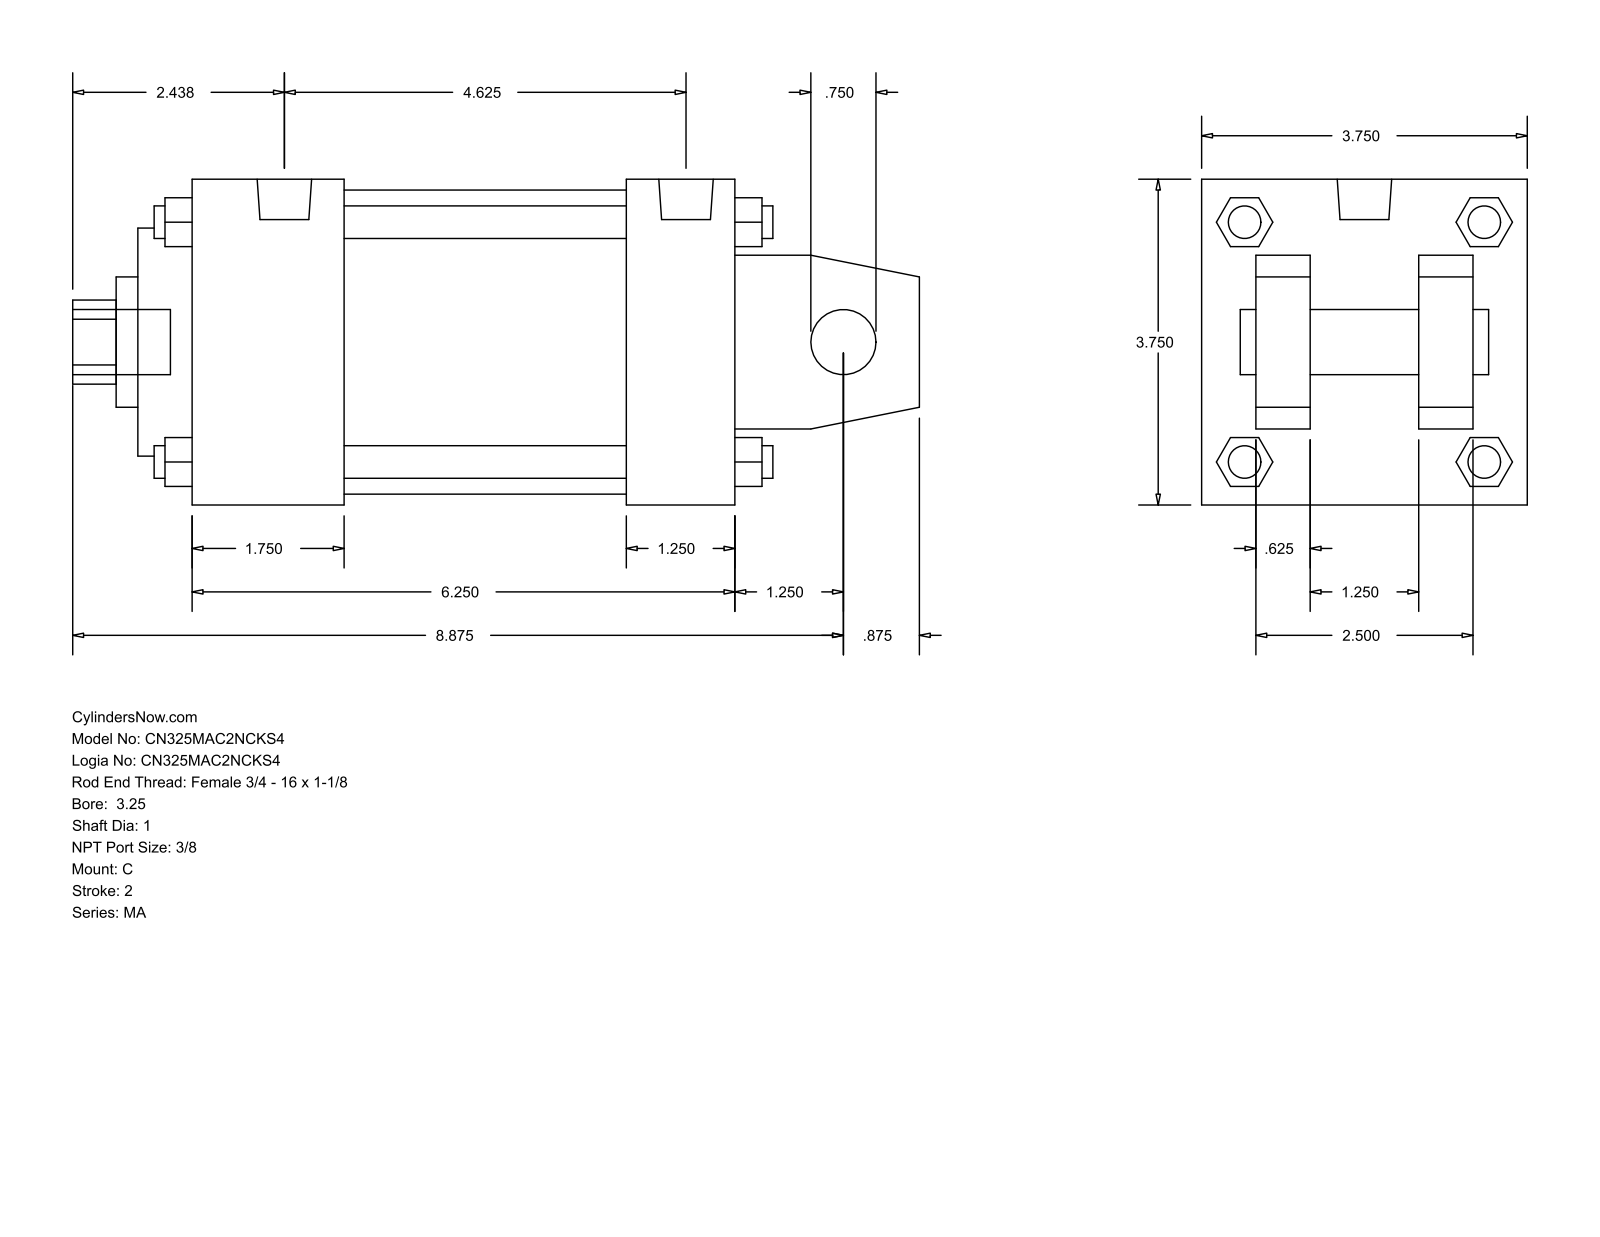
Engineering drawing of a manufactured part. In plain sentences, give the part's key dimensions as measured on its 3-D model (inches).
The part is named "MA_C__0325_1". Its 3-D file was written by "GSSL Pune (CONFIG_CONTROL_DESIGN)". It is 0 solids with 141 faces: 109 planar, 32 cylindrical and 0 other. Overall it measures 9.75 by 3.75 by 3.75 inches. Round holes: 1 of diameter 0.75, 1 of diameter 1, 1 of diameter 1.5, 1 of diameter 2.625, 1 of diameter 3.5. Round bosses or shafts: 4 of diameter 0.437, 4 of diameter 0.375, 2 of diameter 0.627, 1 of diameter 0.75. Partial cylindrical surfaces (rounded edges, fillets, slot ends): 1 of radius 0.484. The main face-to-face distances are 3.75, 0.625, 2.5, 6.25, 1.25, 3.125, 1.875, 5, 1.25, 1.75.
